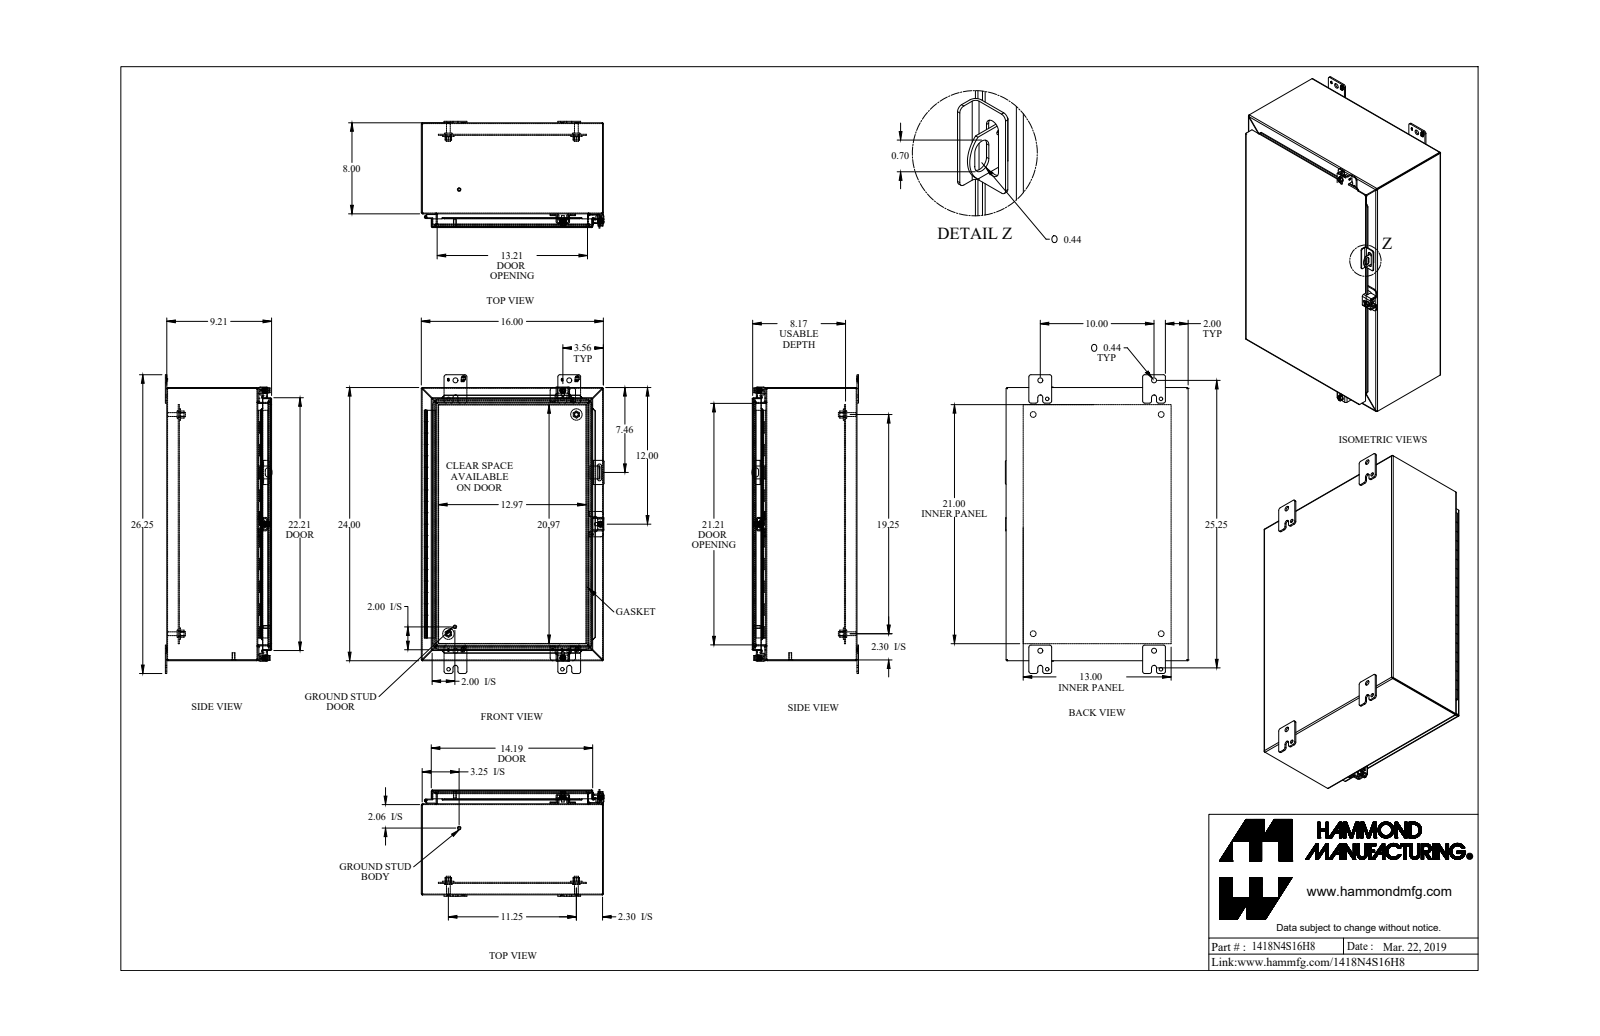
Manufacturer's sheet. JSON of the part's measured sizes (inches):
{"part_name": "1418N4S16H8_Default", "step_written_by": "SolidWorks 2019 (CONFIG_CONTROL_DESIGN)", "units": "inches", "bodies": {"solids": 35, "faces": 1254, "planar": 682, "cylindrical": 444, "other": 128}, "overall_size": [26.25, 16.063, 9.375], "volume_in3": 152.8, "surface_area_in2": 4057, "round_holes": [[0.313, 4], [0.437, 4], [0.5, 4], [0.213, 3], [0.375, 3], [0.265, 2], [0.307, 2], [0.445, 2], [0.11, 1], [0.125, 1], [0.265, 1]], "round_bosses_or_shafts": [[0.65, 4], [0.375, 4], [0.332, 4], [0.5, 3], [0.39, 3], [0.244, 3], [1, 2], [0.313, 2]], "partial_cylinders_radius": [[0.188, 26], [0.036, 24], [0.108, 24], [0.25, 16], [0.048, 15], [0.143, 15], [0.125, 10], [0.045, 8]], "face_to_face_distances": [0.072, 15.928, 0.072, 9.066, 9.138, 9.138, 0.937, 9.21, 1.009, 0.095], "hole_center_spacings": [10, 1.735, 9.857, 10.285, 10.731, 11.25, 16.478, 19.25]}
